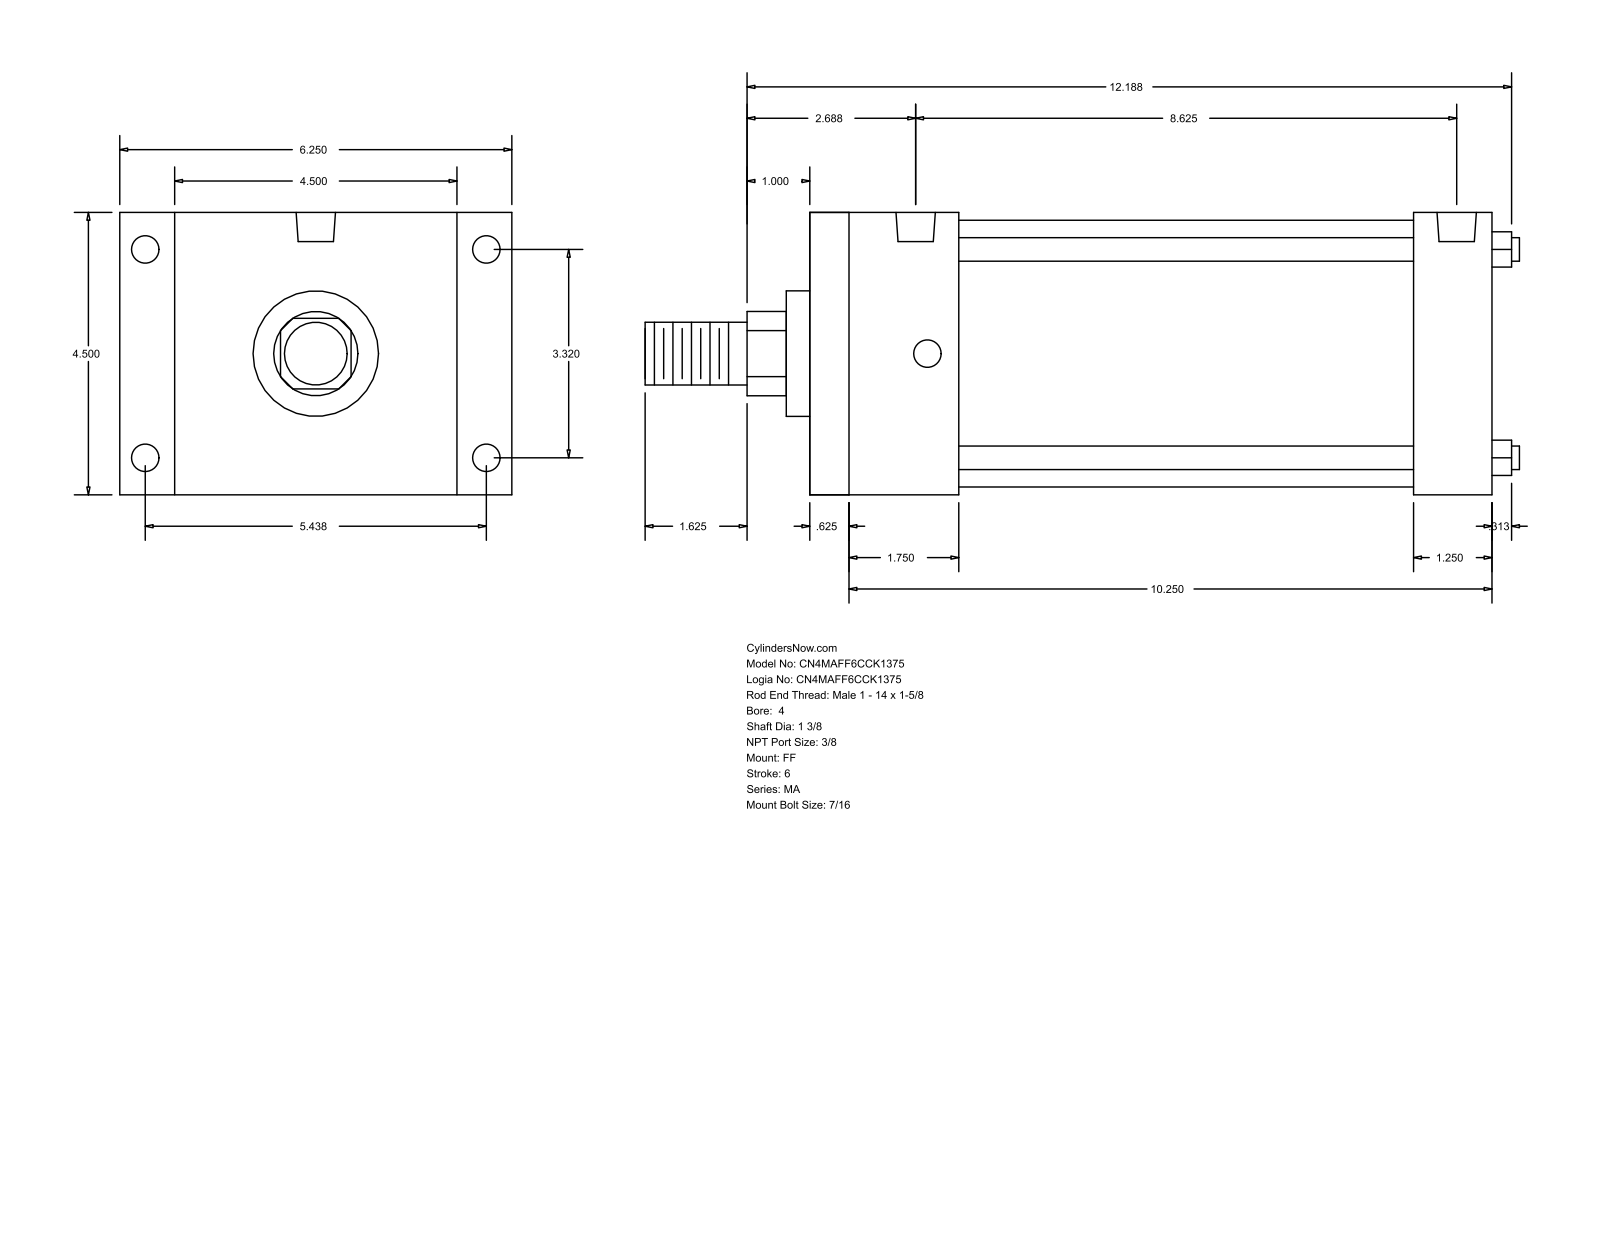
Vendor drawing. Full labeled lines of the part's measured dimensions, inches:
Part name (STEP PRODUCT): MA_FF__0400_1.375
STEP written by: GSSL Pune (CONFIG_CONTROL_DESIGN)
Units: inches
Bodies: 0 solids, 92 faces (64 planar, 28 cylindrical, 0 other)
Overall size (bounding box): 13.937 × 6.25 × 4.5
Round holes (diameter × count): ⌀0.437 ×8, ⌀0.627 ×2
Round bosses / shafts (diameter × count): ⌀0.375 ×4, ⌀4.25 ×1, ⌀2 ×1, ⌀1.375 ×1, ⌀1 ×1
Partial cylindrical surfaces — rounded edges, fillets, slot ends (radius × count): R0.672 ×1
Main face-to-face distances: 4.5, 10.875, 0.625, 10.25, 0.875, 5.375, 9.625, 9, 1.25, 2.375
Hole centre spacings: 0.188, 3.32, 5.438, 6.371, 8.25, 8.437, 8.625
